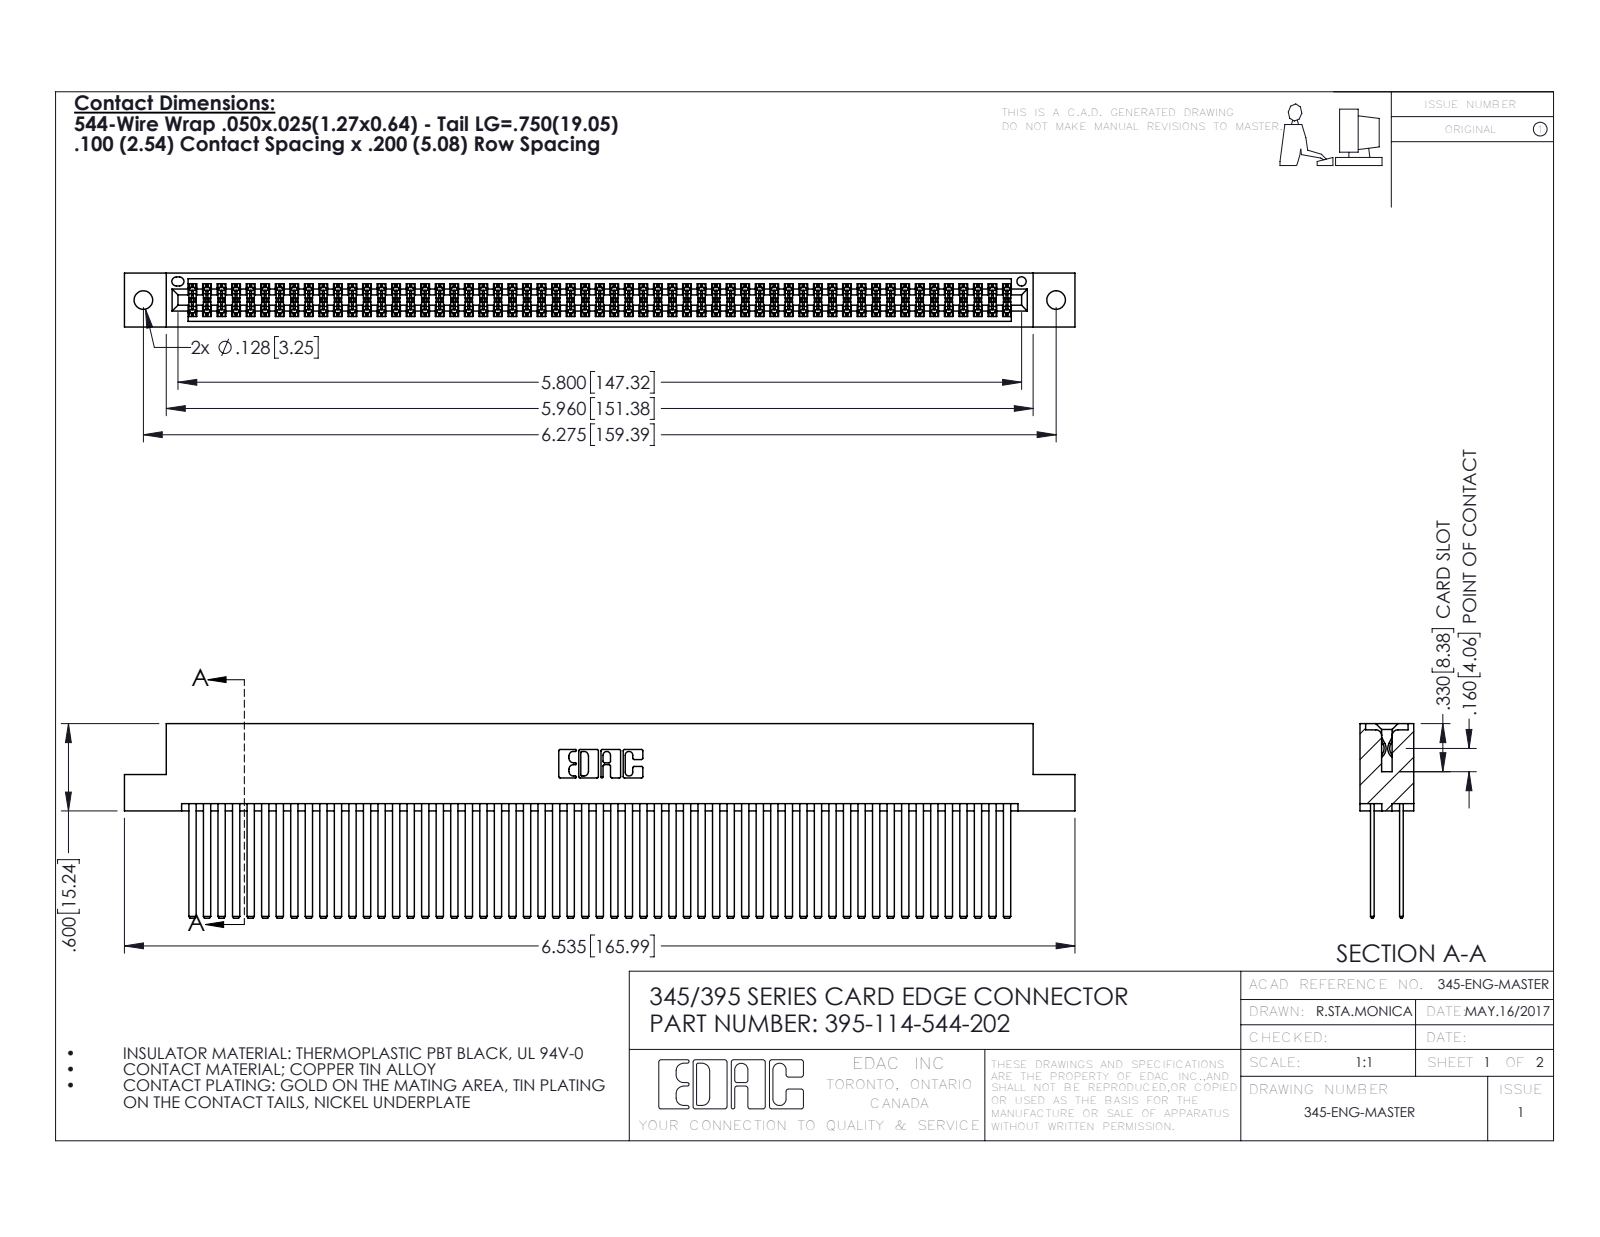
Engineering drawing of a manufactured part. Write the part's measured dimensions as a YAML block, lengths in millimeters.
part_name: "345 Part_Flush Mounting Lugs - 0.128 Dia; 345-292-001_345-293-144; 395-114-544-202"
step_written_by: "SolidWorks 2016 (CONFIG_CONTROL_DESIGN)"
units: millimeters
bodies: {solids: 115, faces: 5142, planar: 3386, cylindrical: 1756, other: 0}
overall_size: [166, 34, 9.4]
volume: 17830
surface_area: 31050
round_holes:
  - {diameter: 3.3, count: 2}
  - {diameter: 1.6, count: 1}
partial_cylinders:
  - {radius: 0.2, count: 171}
  - {radius: 0.3, count: 22}
  - {radius: 0.2, count: 6}
  - {radius: 0.8, count: 6}
  - {radius: 0.7, count: 3}
  - {radius: 0.4, count: 2}
  - {radius: 0.5, count: 2}
  - {radius: 0.6, count: 2}
face_to_face_distances: [5.1, 0.6, 7.6, 1.8, 2.5, 6.9, 5.7, 4.4, 9.4, 1.3]
hole_center_spacings: [6.9, 153.4, 159.4]
